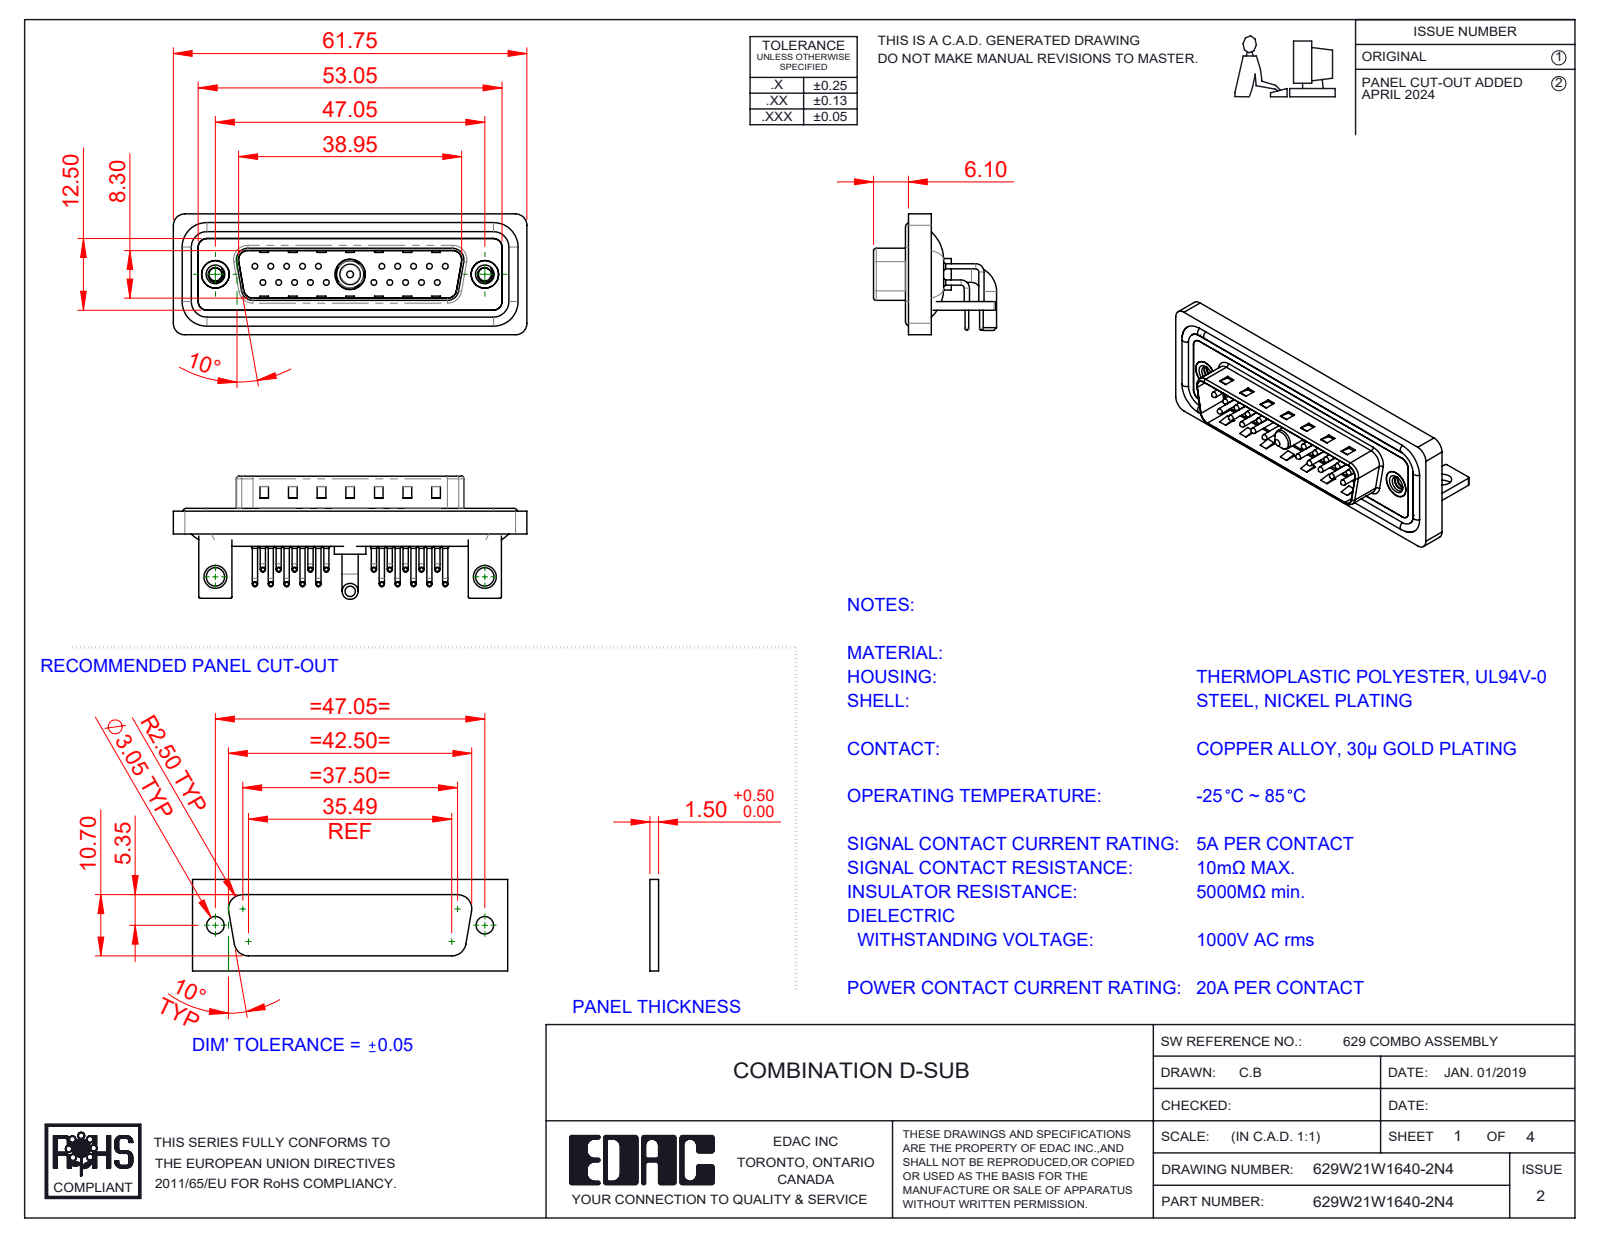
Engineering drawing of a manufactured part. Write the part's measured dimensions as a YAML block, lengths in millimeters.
part_name: "629Combo Contact Row 2; 629Combo Housing_21W1; 629W21W1640-2N4; 629Combo Shell Rear_25 Contacts (+6 more)"
step_written_by: "SolidWorks 2023 (CONFIG_CONTROL_DESIGN)"
units: millimeters
bodies: {solids: 31, faces: 2766, planar: 1519, cylindrical: 947, other: 300}
overall_size: [61.75, 21.5, 21.1]
volume: 7695
surface_area: 13308
round_holes:
  - {diameter: 0.75, count: 20}
  - {diameter: 1.6, count: 20}
  - {diameter: 2, count: 20}
  - {diameter: 2.26, count: 2}
  - {diameter: 3.2, count: 2}
  - {diameter: 4, count: 2}
  - {diameter: 4.8, count: 2}
  - {diameter: 5, count: 2}
  - {diameter: 4.85, count: 1}
  - {diameter: 5.3, count: 1}
round_bosses_or_shafts:
  - {diameter: 0.9, count: 40}
  - {diameter: 1.5, count: 20}
  - {diameter: 1, count: 20}
  - {diameter: 0.65, count: 20}
  - {diameter: 1.6, count: 4}
  - {diameter: 4.9, count: 2}
  - {diameter: 2.8, count: 2}
  - {diameter: 5.5, count: 1}
partial_cylinders:
  - {radius: 1.01, count: 20}
  - {radius: 2, count: 19}
  - {radius: 1.5, count: 18}
  - {radius: 0.25, count: 16}
  - {radius: 0.5, count: 9}
  - {radius: 1.6, count: 8}
  - {radius: 0.6, count: 4}
  - {radius: 0.65, count: 4}
face_to_face_distances: [0.4, 0.8, 2.1, 2.9, 1.5, 1.1, 4.1, 1.6, 4.5, 3.7]
hole_center_spacings: [3.16, 2.77, 5.54, 8.31, 5.04, 19.39, 20.97, 22.16]
